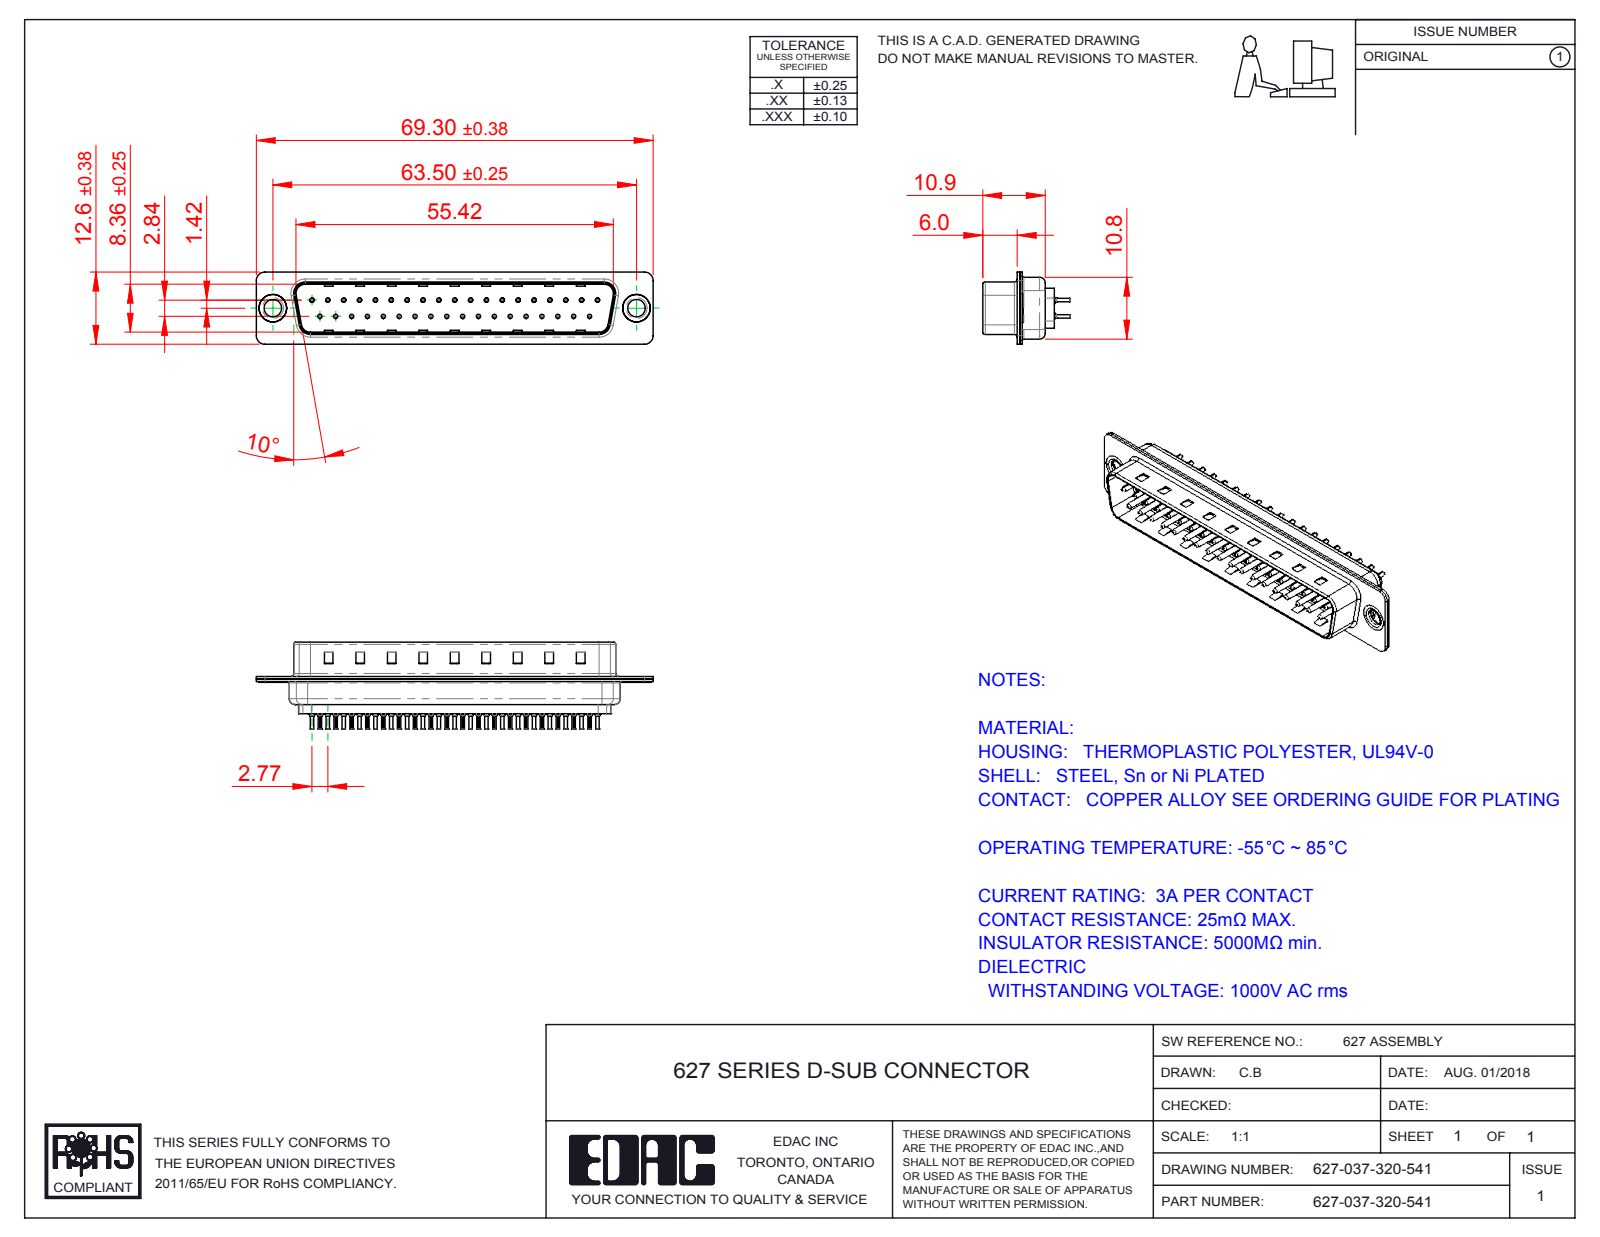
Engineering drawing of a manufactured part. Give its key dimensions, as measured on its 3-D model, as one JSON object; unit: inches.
{"part_name": "627 Shell Front_37 Contacts; 627 Thru Hole Rivet; 627 Contact Row 1_20L; 627 Housing_37 LP (+3 more)", "step_written_by": "SolidWorks 2016 (CONFIG_CONTROL_DESIGN)", "units": "inches", "bodies": {"solids": 42, "faces": 4012, "planar": 1091, "cylindrical": 1494, "other": 1427}, "overall_size": [2.728, 0.598, 0.496], "volume_in3": 0.22, "surface_area_in2": 15.98, "round_holes": [[0.008, 37], [0.014, 37], [0.043, 37], [0.063, 37], [0.12, 2], [0.157, 2], [0.189, 2]], "round_bosses_or_shafts": [[0.079, 37], [0.059, 37], [0.03, 37], [0.024, 37], [0.197, 2], [0.193, 2], [0.14, 2]], "partial_cylinders_radius": [[0.004, 74], [0.059, 16], [0.079, 12], [0.02, 8], [0.063, 8], [0.01, 4], [0.024, 4], [0.026, 4]], "face_to_face_distances": [0.016, 0.032, 0.377, 0.018, 0.345, 0.059, 0.035, 0.055, 0.238, 0.02], "hole_center_spacings": [0.124, 0.109, 0.218, 0.327, 0.198, 0.398, 0.436, 0.503]}
